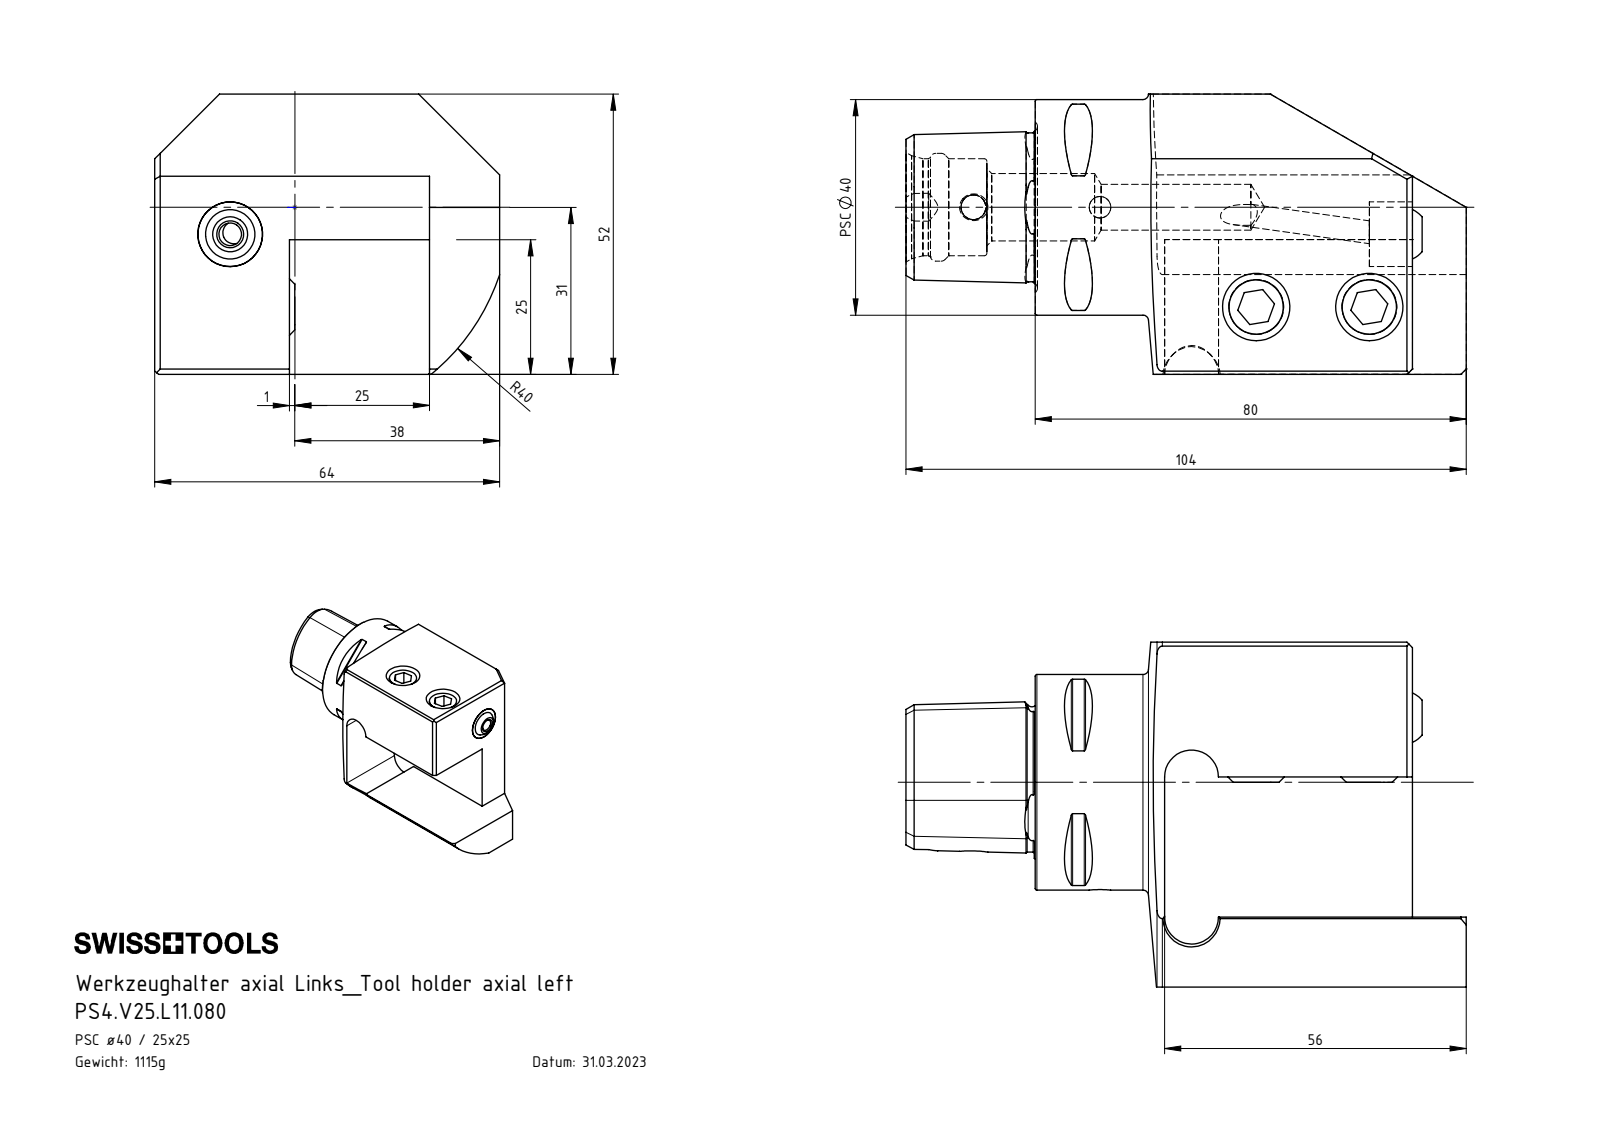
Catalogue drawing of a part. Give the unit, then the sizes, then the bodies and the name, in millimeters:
Units: millimetres
Overall size (bounding box): 104 × 64 × 52
Round holes (diameter × count): ⌀4.2 ×2, ⌀10.2 ×2, ⌀4 ×1, ⌀4.6 ×1, ⌀7 ×1, ⌀8.5 ×1, ⌀12 ×1, ⌀12.5 ×1, ⌀18 ×1, ⌀20 ×1
Round bosses / shafts (diameter × count): ⌀12 ×2, ⌀40 ×1
Partial cylindrical surfaces — rounded edges, fillets, slot ends (radius × count): R0.3 ×8, R5 ×2, R3 ×1, R40 ×1
Main face-to-face distances: 25, 51, 13, 64, 26, 27, 52, 39, 24, 46
Hole centre spacings: 13, 21, 23.5, 34.4, 53.31, 55.66, 75.79
Volume: 142 413 mm³ · Surface area: 31 142 mm²
Bodies: 5 solids, 216 faces (58 planar, 49 cylindrical, 109 other)
Part name (STEP PRODUCT): KU1-U12.001.010_2; KU1-U12.001.010_1; ISO 4026 - M12 x 25; PS4.V25.L11.080 (+2 more)
STEP written by: SolidWorks 2017 (AUTOMOTIVE_DESIGN)
